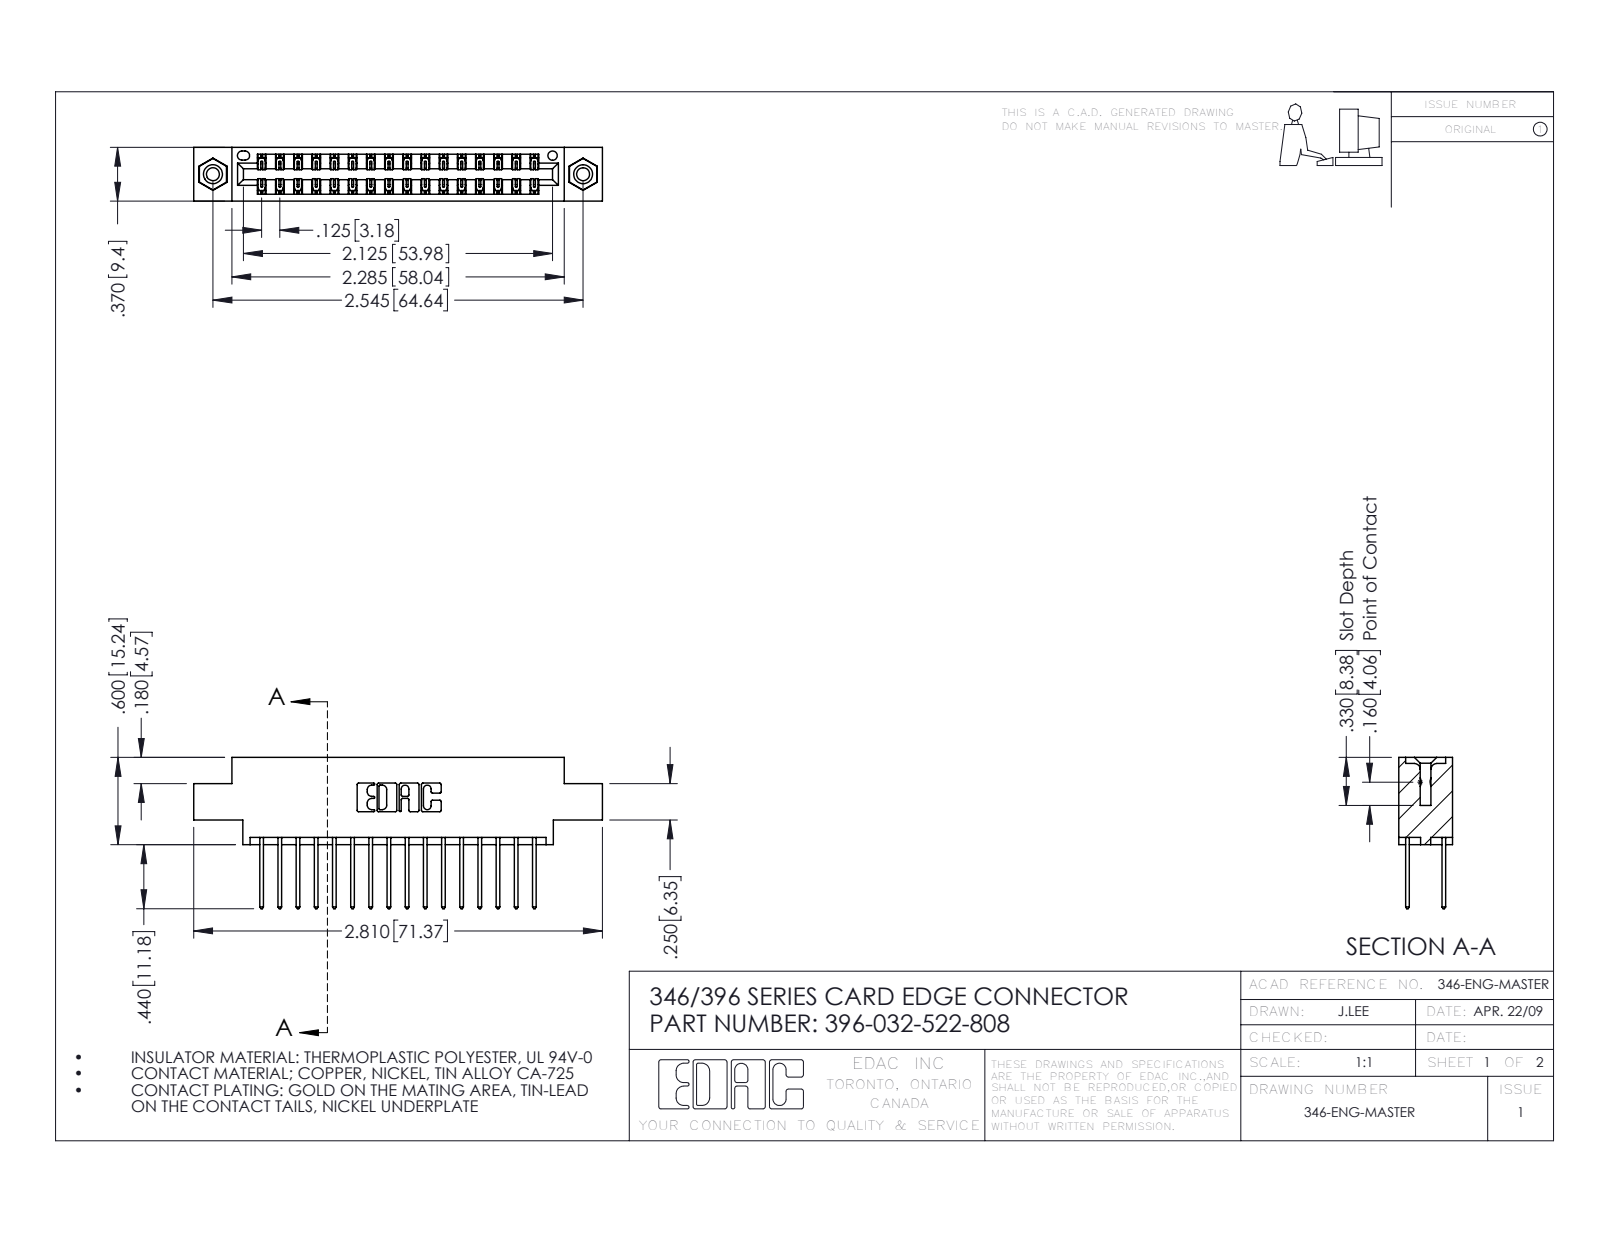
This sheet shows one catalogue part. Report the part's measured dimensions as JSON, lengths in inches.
{"part_name": "345-250-001_345-250-003-102; 345-292-001_345-293-122; 346 Part_0.170 Offset - 0.156 Dia-TI; 396-032-522-808", "step_written_by": "SolidWorks 2016 (CONFIG_CONTROL_DESIGN)", "units": "inches", "bodies": {"solids": 35, "faces": 1850, "planar": 1232, "cylindrical": 602, "other": 16}, "overall_size": [2.81, 1.04, 0.37], "volume_in3": 0.408, "surface_area_in2": 14.49, "round_holes": [[0.089, 2], [0.125, 2], [0.156, 2], [0.064, 1]], "round_bosses_or_shafts": [[0.155, 2]], "partial_cylinders_radius": [[0.006, 48], [0.01, 32], [0.01, 22], [0.007, 6], [0.031, 6], [0.026, 3], [0.014, 2], [0.022, 2]], "face_to_face_distances": [0.048, 0.322, 0.25, 0.37, 0.072, 0.298, 0.025, 0.275, 0.222, 0.148], "hole_center_spacings": [0.246, 2.338, 2.545]}
